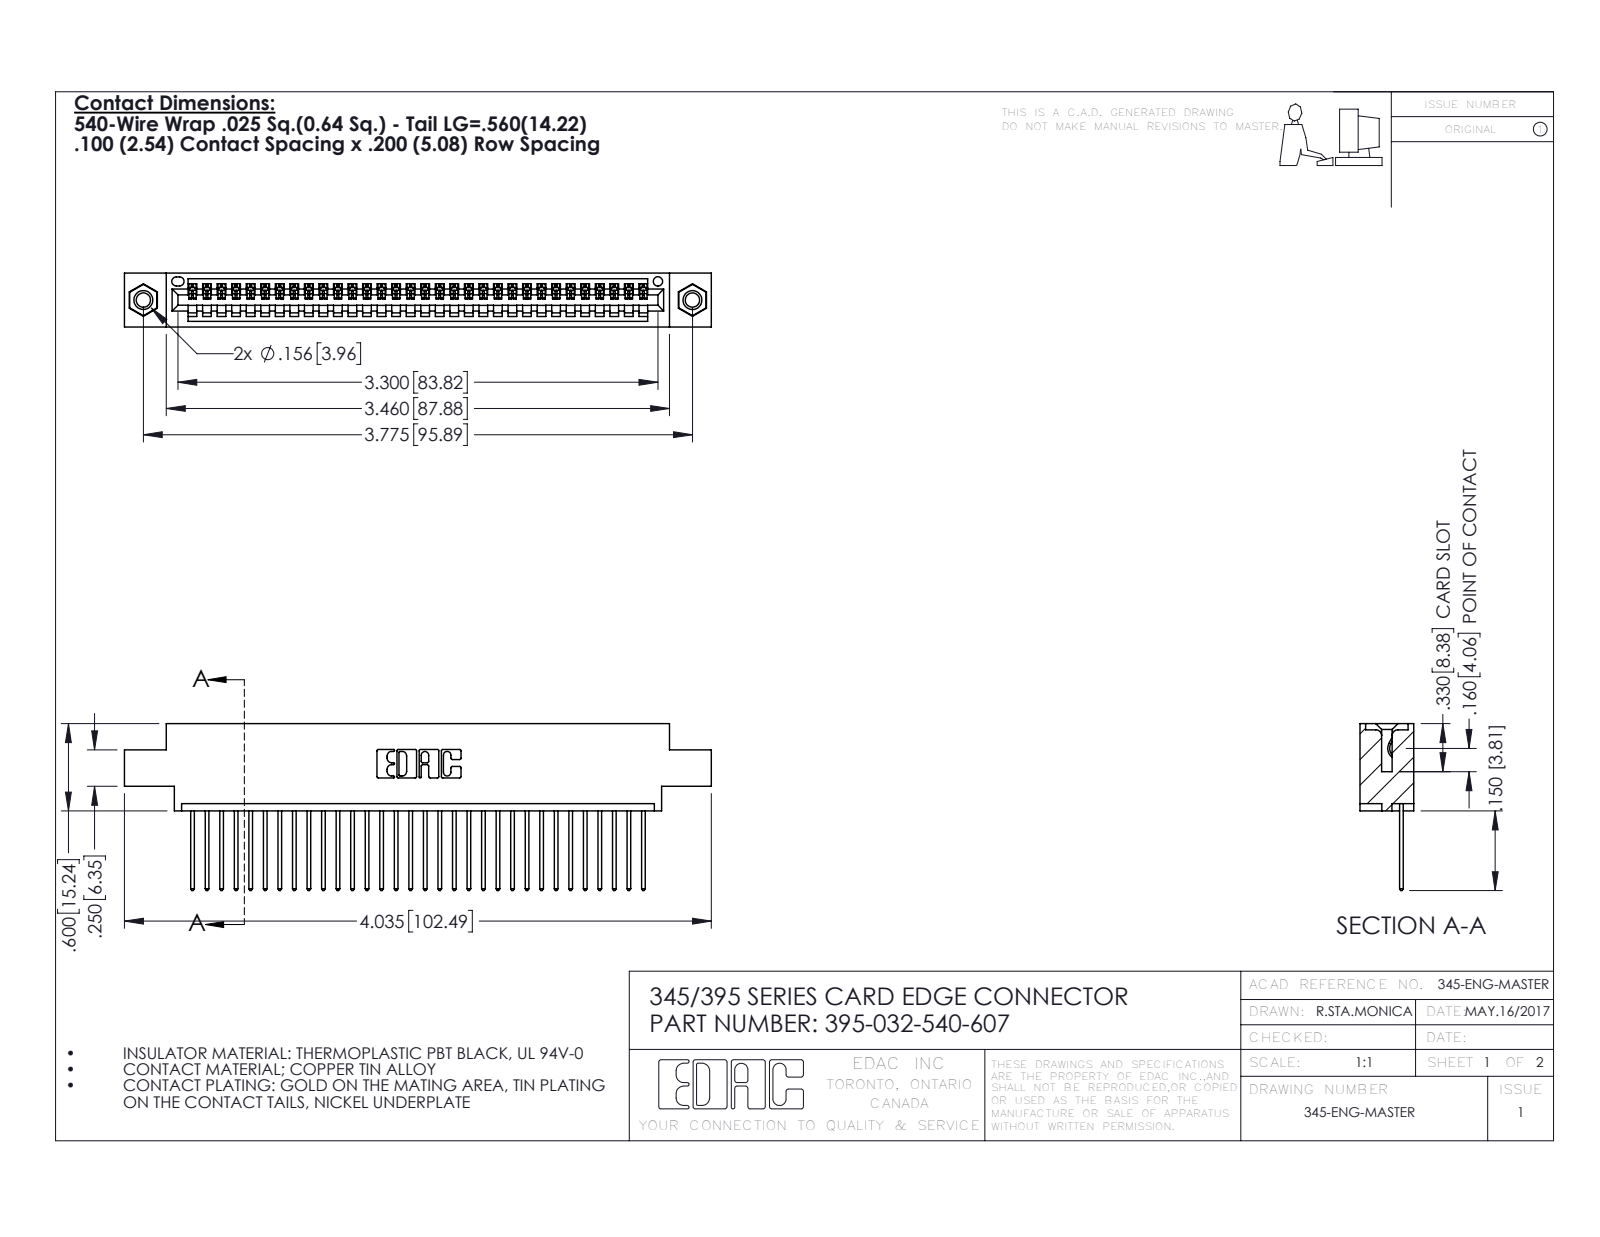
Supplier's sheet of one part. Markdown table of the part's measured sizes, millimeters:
| quantity | value |
| --- | --- |
| part name | 345 Part_0.170 Offset - 0.156 Dia-TI; 345-250-001_345-250-005-103; 345-292-001_345-293-140; 395-032-540-607 |
| STEP written by | SolidWorks 2016 (CONFIG_CONTROL_DESIGN) |
| units | millimeters |
| bodies | 35 solids, 2046 faces (1396 planar, 634 cylindrical, 16 other) |
| overall size | 102.5 × 29.1 × 9.4 |
| volume | 9 570 mm³ |
| surface area | 13 050 mm² |
| round holes (diameter × count) | 2.5 × 2, 3.2 × 2, 4 × 2, 1.6 × 1 |
| round bosses / shafts (diameter × count) | 3.9 × 2 |
| partial cylindrical surfaces (radius × count) | 0.2 × 64, 0.3 × 64, 0.3 × 22, 0.2 × 6, 0.8 × 6, 0.7 × 3, 0.8 × 2, 1 × 2 |
| main face-to-face distances | 1.8, 7.6, 9.4, 2.5, 6.9, 0.6, 5.1, 5.7, 4.4, 3.8 |
| hole center spacings | 6.9, 89.9, 95.9 |
